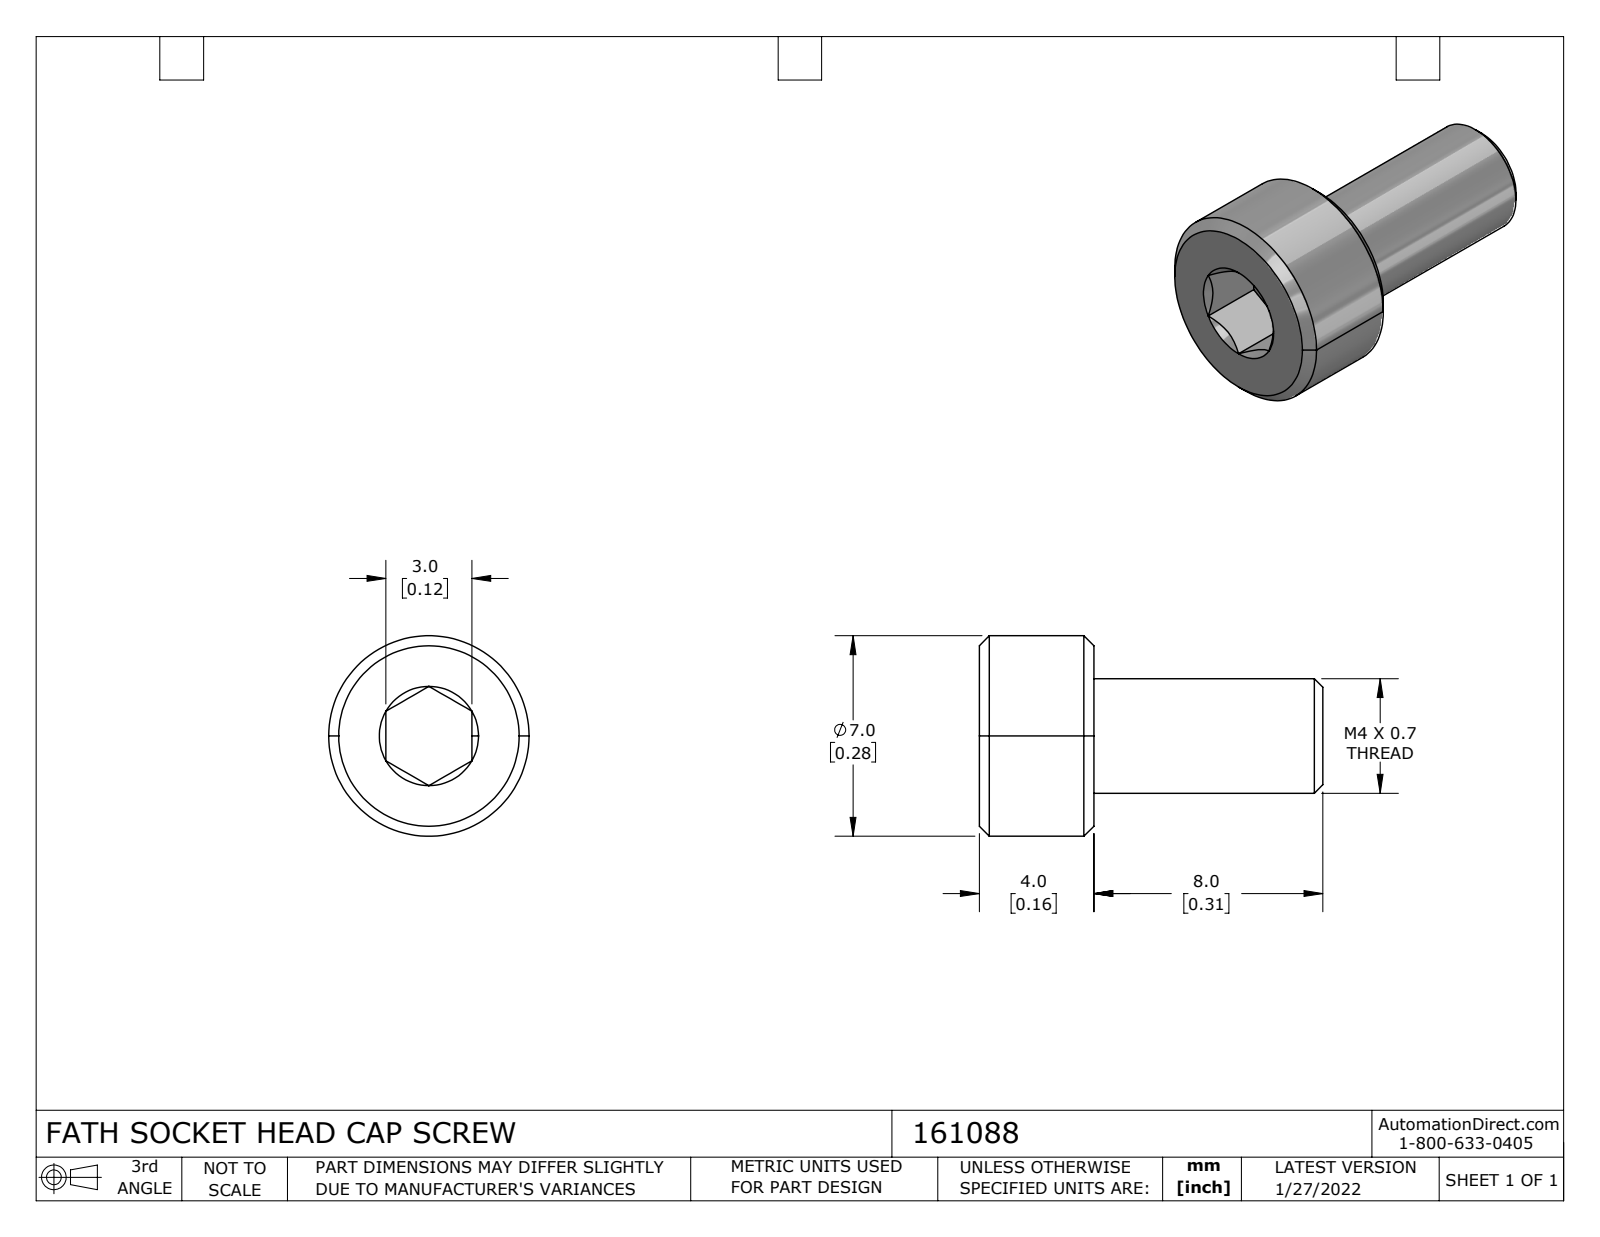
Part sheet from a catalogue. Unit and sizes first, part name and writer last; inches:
Units: inches
Overall size (bounding box): 0.472 × 0.276 × 0.276
Round bosses / shafts (diameter × count): ⌀0.276 ×1, ⌀0.157 ×1
Main face-to-face distances: 0.157, 0.118, 0.472, 0.315, 0.089, 0.069, 0.384
Volume: 0.014 in³ · Surface area: 0.428 in²
Bodies: 1 solid, 27 faces (10 planar, 4 cylindrical, 13 other)
Part name (STEP PRODUCT): 161088
STEP written by: SolidWorks 2021 (CONFIG_CONTROL_DESIGN)
